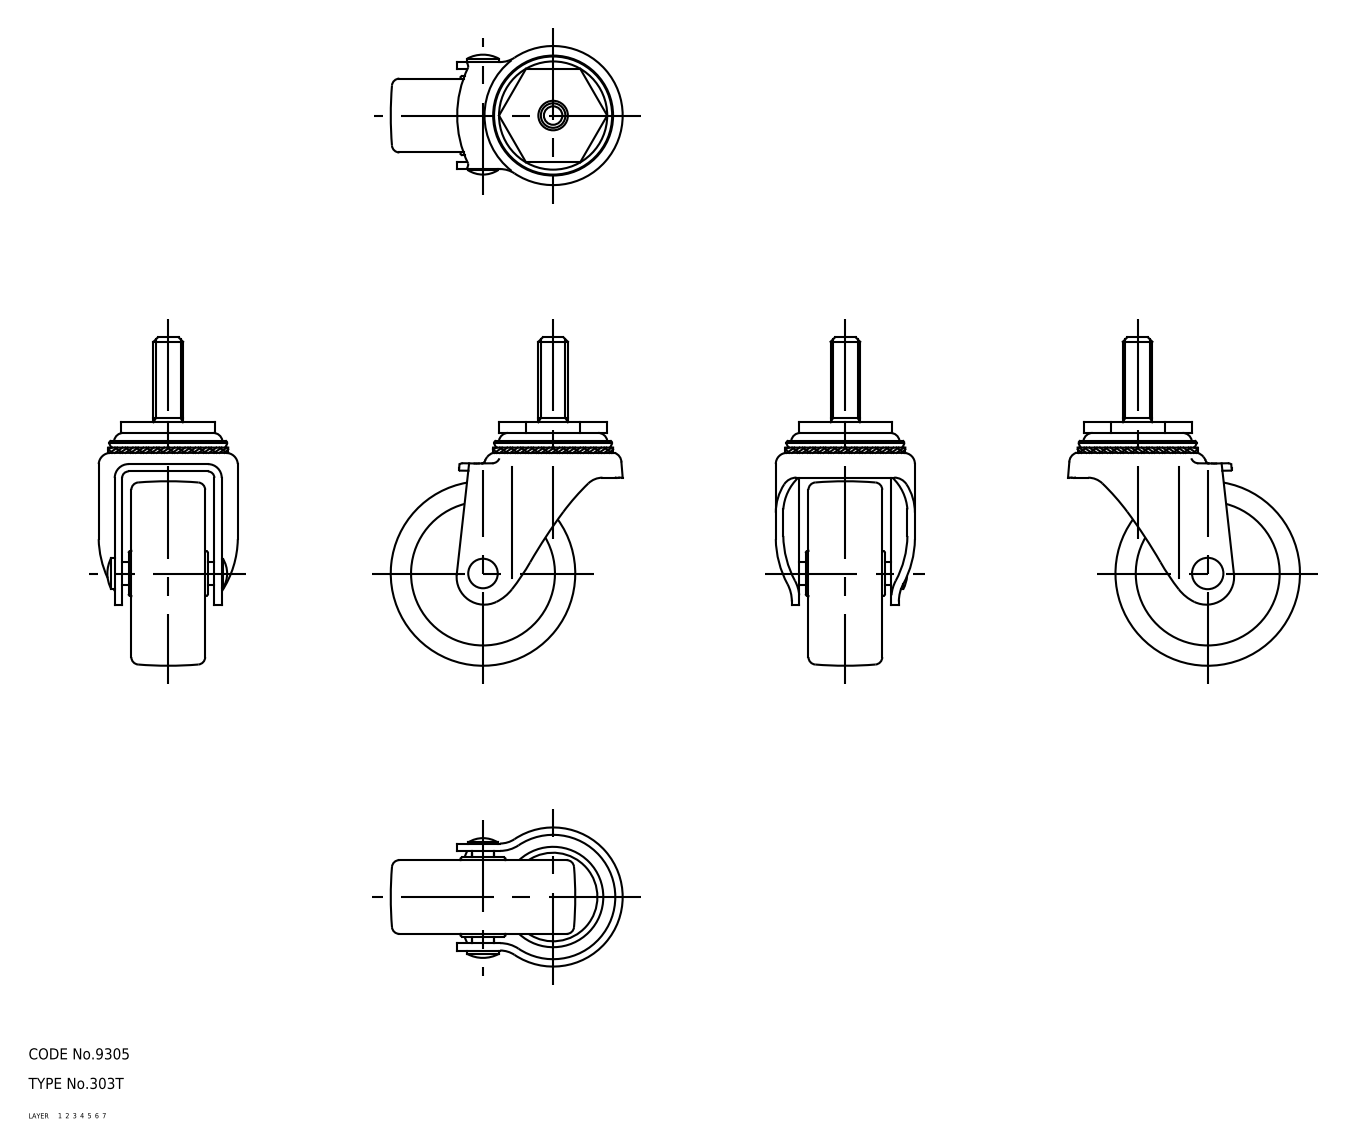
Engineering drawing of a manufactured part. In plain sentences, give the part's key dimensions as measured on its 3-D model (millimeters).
The part is named "wheel; main shaft; axle; No_303T_23335_36". Its 3-D file was written by "CADfix (AUTOMOTIVE_DESIGN)". It is 5 solids with 182 faces: 0 planar, 0 cylindrical and 182 other. Overall it measures 89 by 62.85 by 37.7 millimeters. Its volume is 49 059 cubic millimeters and its surface area 18 668 square millimeters.
